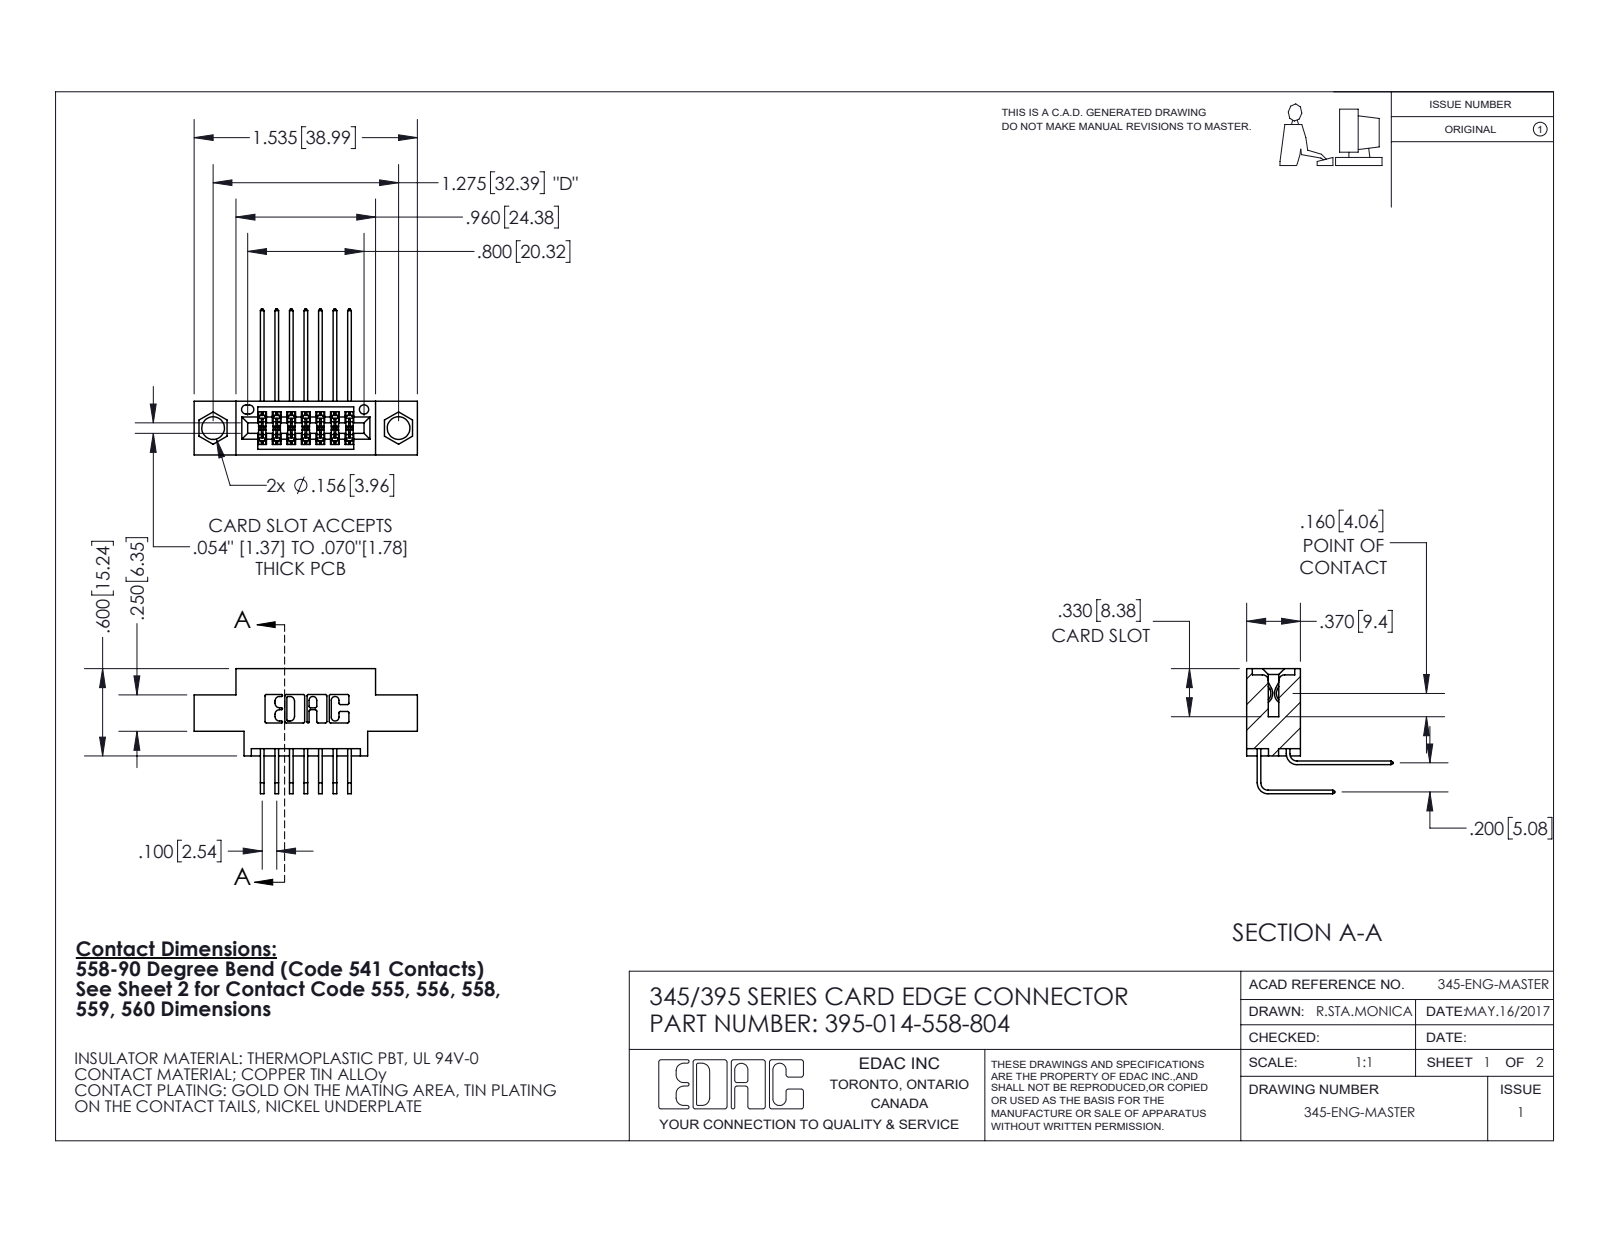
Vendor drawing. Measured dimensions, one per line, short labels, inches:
name: 345-292-001_558 Tail - 2; 345-292-001_558 559 Tail - 1; 395-014-558-804; 345 Part_0.170 Offset - 0.156 Dia-TI
written by: SolidWorks 2020 (CONFIG_CONTROL_DESIGN)
unit: in
bodies: 15 solids, 872 faces (588 planar, 284 cylindrical, 0 other)
size: 1.535 × 1.005 × 0.859
volume: 0.203 in³; area: 7.146 in²
holes: 2× ⌀0.156, 1× ⌀0.064
rounds: 22× R0.01, 21× R0.006, 6× R0.007, 6× R0.031, 3× R0.026, 2× R0.014, 2× R0.019, 2× R0.022
face distances: 0.2, 0.37, 0.072, 0.298, 0.1, 0.098, 0.272, 0.025, 0.3, 0.06
hole spacings: 0.27, 1.045, 1.275
